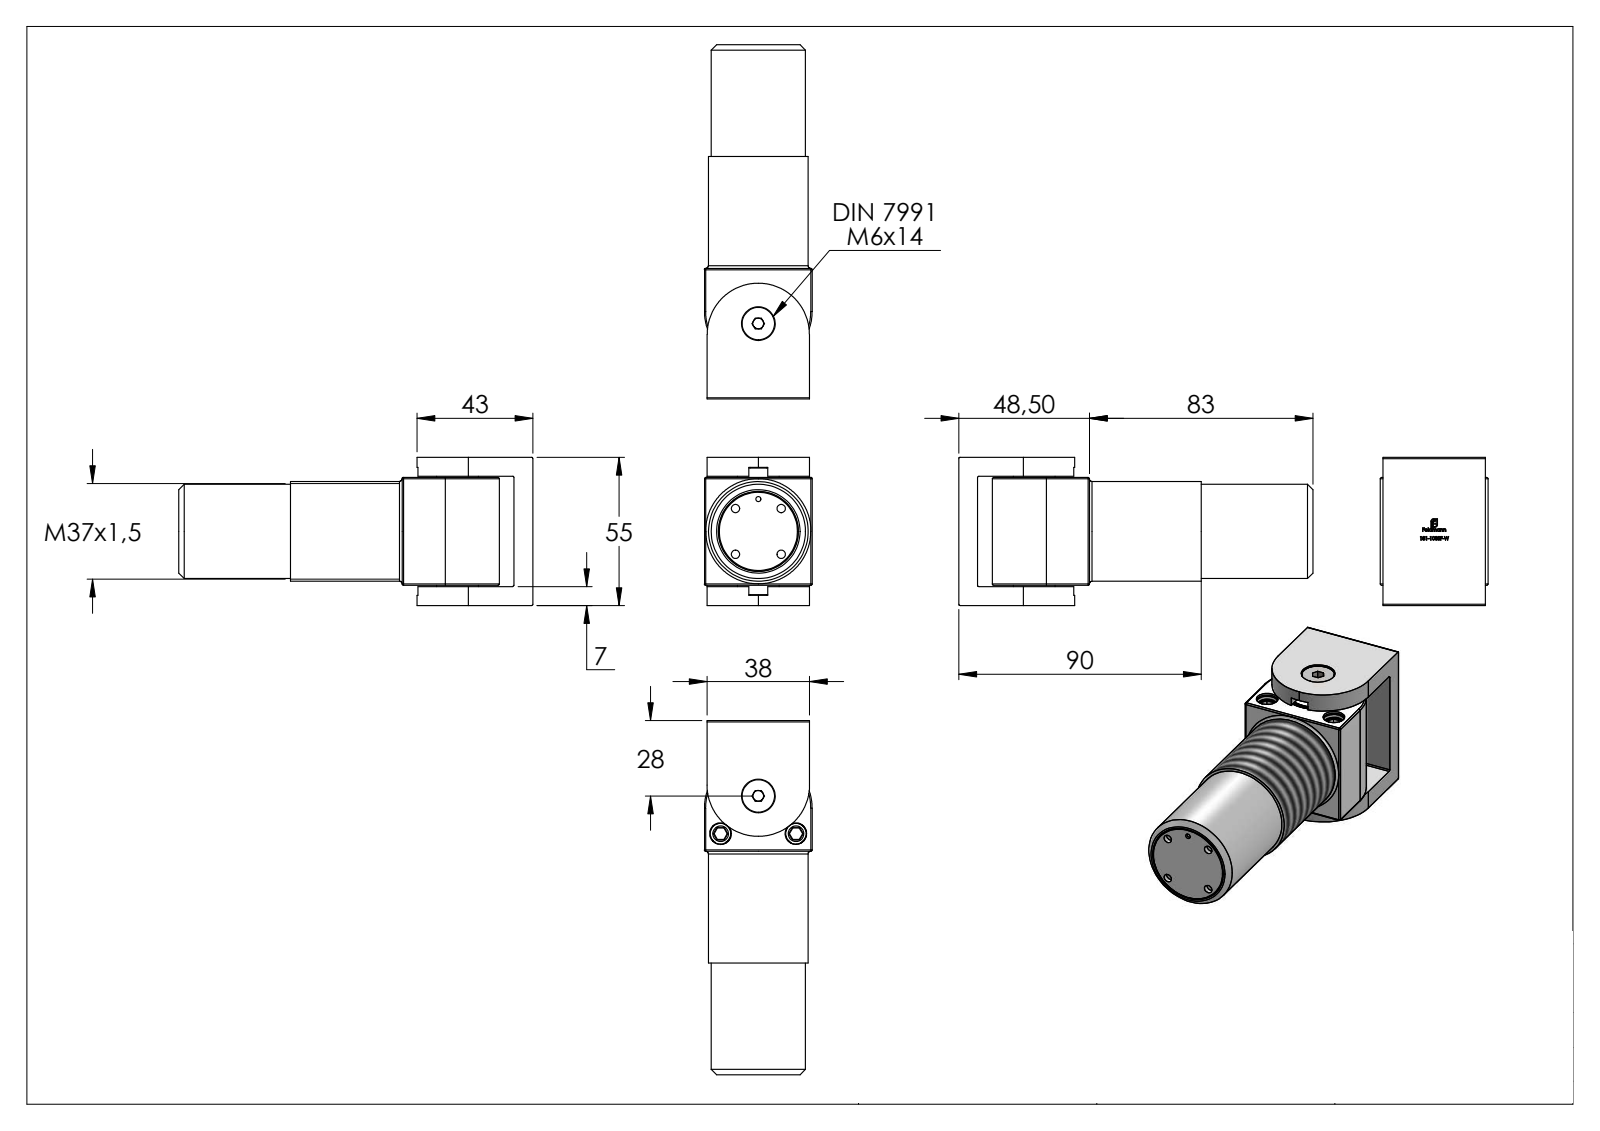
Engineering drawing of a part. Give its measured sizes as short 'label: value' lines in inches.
name: DIN-7991 M3-M10_DIN7991 M6x14; 181-108SF-W; Teil2_181-108SF-W Teil2; DIN-7991 M3-M10 (+3 more)
written by: SolidWorks 2018 (CONFIG_CONTROL_DESIGN)
unit: in
bodies: 6 solids, 549 faces (263 planar, 88 cylindrical, 198 other)
size: 551.199 × 236.22 × 236.22
volume: 10.1 in³; area: 49.08 in²
holes: 4× ⌀0.122, 2× ⌀0.315, 1× ⌀0.075, 1× ⌀0.197, 1× ⌀0.256, 1× ⌀0.492, 1× ⌀0.618, 1× ⌀0.945, 1× ⌀1.169
bosses: 2× ⌀0.307, 1× ⌀1.457, 1× ⌀1.378, 1× ⌀1.161, 1× ⌀1.024, 1× ⌀0.929, 1× ⌀0.61, 1× ⌀0.472
rounds: 12× R0.02, 1× R0.748, 1× R0.787
face distances: 0.276, 1.89, 1.87, 0.02, 0.295, 1.594, 2.165, 1.575, 0.039, 1.535
hole spacings: 0.473, 0.669, 0.362, 0.78, 0.873, 0.945, 0.472, 1.102
